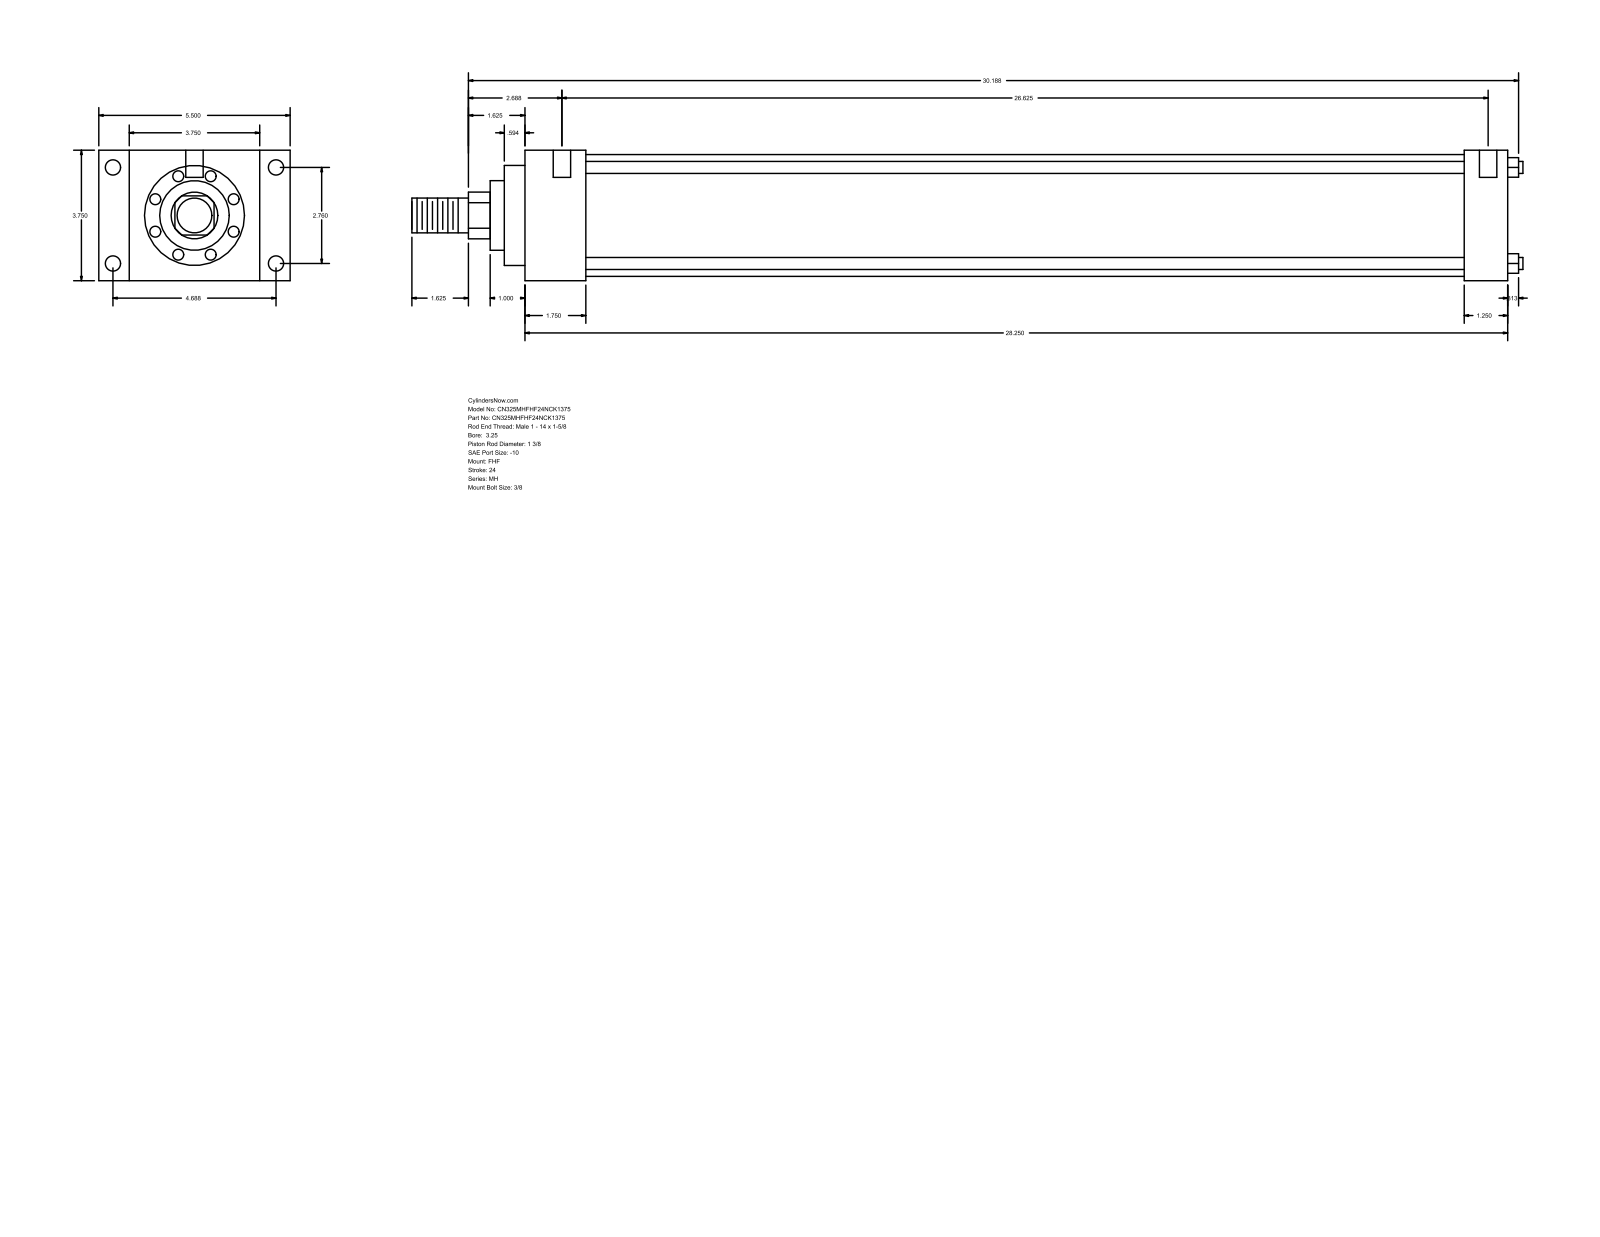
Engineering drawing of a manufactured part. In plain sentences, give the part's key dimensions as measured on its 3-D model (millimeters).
The part is named "MH_FHF__0325_1.375". Its 3-D file was written by "GSSL Pune (CONFIG_CONTROL_DESIGN)". It is 0 solids with 90 faces: 61 planar, 29 cylindrical and 0 other. Overall it measures 811.21 by 139.7 by 95.25 millimeters. Round holes: 4 of diameter 5.56, 4 of diameter 11.13, 2 of diameter 12.7. Round bosses or shafts: 4 of diameter 8.76, 1 of diameter 88.9, 1 of diameter 73.03, 1 of diameter 50.8, 1 of diameter 34.92, 1 of diameter 25.4. Partial cylindrical surfaces (rounded edges, fillets, slot ends): 1 of radius 17.06. The main face-to-face distances are 95.24, 717.56, 44.45, 673.11, 22.23, 117.47, 139.7, 685.81, 641.36, 31.75. The hole center spacings are 70.1, 119.06, 138.16, 682.63, 1.59, 4.76, 676.28, 677.87.
